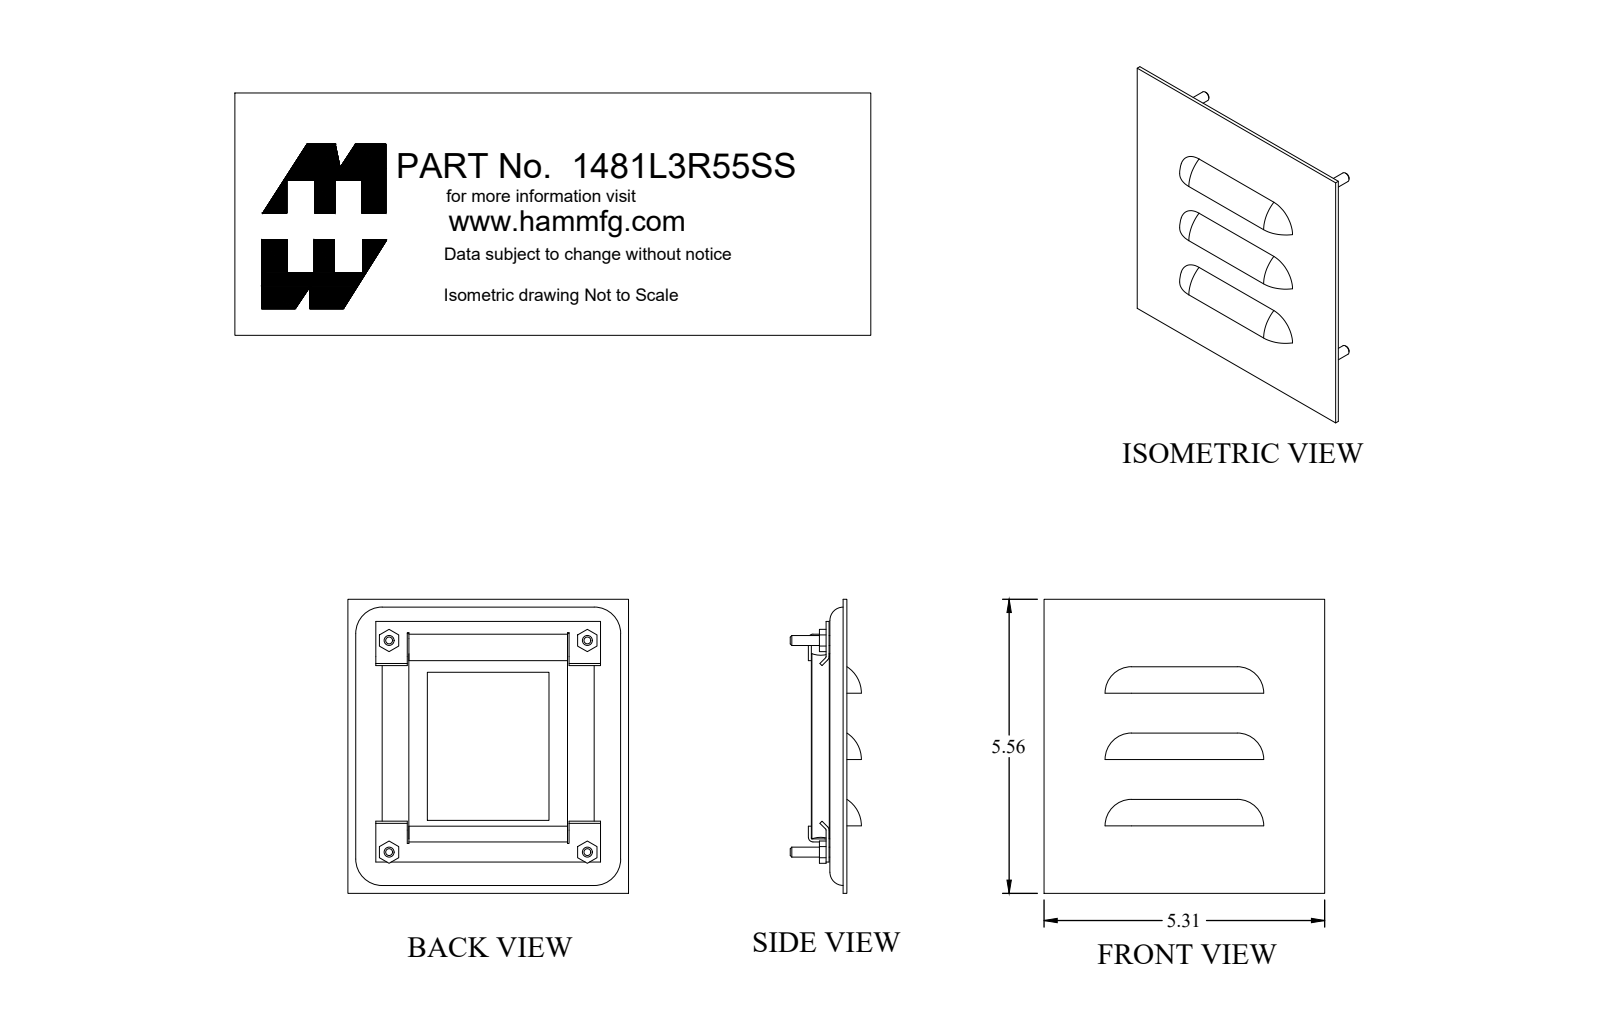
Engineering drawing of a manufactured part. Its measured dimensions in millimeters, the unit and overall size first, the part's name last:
Units: millimetres
Overall size (bounding box): 141.2 × 134.8 × 25.5
Round holes (diameter × count): ⌀4 ×5, ⌀5.2 ×4
Round bosses / shafts (diameter × count): ⌀6.4 ×4, ⌀4.8 ×4
Partial cylindrical surfaces — rounded edges, fillets, slot ends (radius × count): R0.7 ×6, R2.2 ×6, R6.4 ×4, R11.9 ×4, R12.7 ×4, R13.3 ×3, R15.1 ×3
Main face-to-face distances: 1.8, 7.6, 6.4, 1.3, 1.9, 8.2, 1.4, 9.4, 15.8, 14
Hole centre spacings: 101.6, 95.3, 95.3, 139.3, 139.3
Volume: 122 500 mm³ · Surface area: 98 710 mm²
Bodies: 14 solids, 251 faces (146 planar, 73 cylindrical, 32 other)
Part name (STEP PRODUCT): 1481L3R55SS_Default
STEP written by: SolidWorks 2019 (CONFIG_CONTROL_DESIGN)
